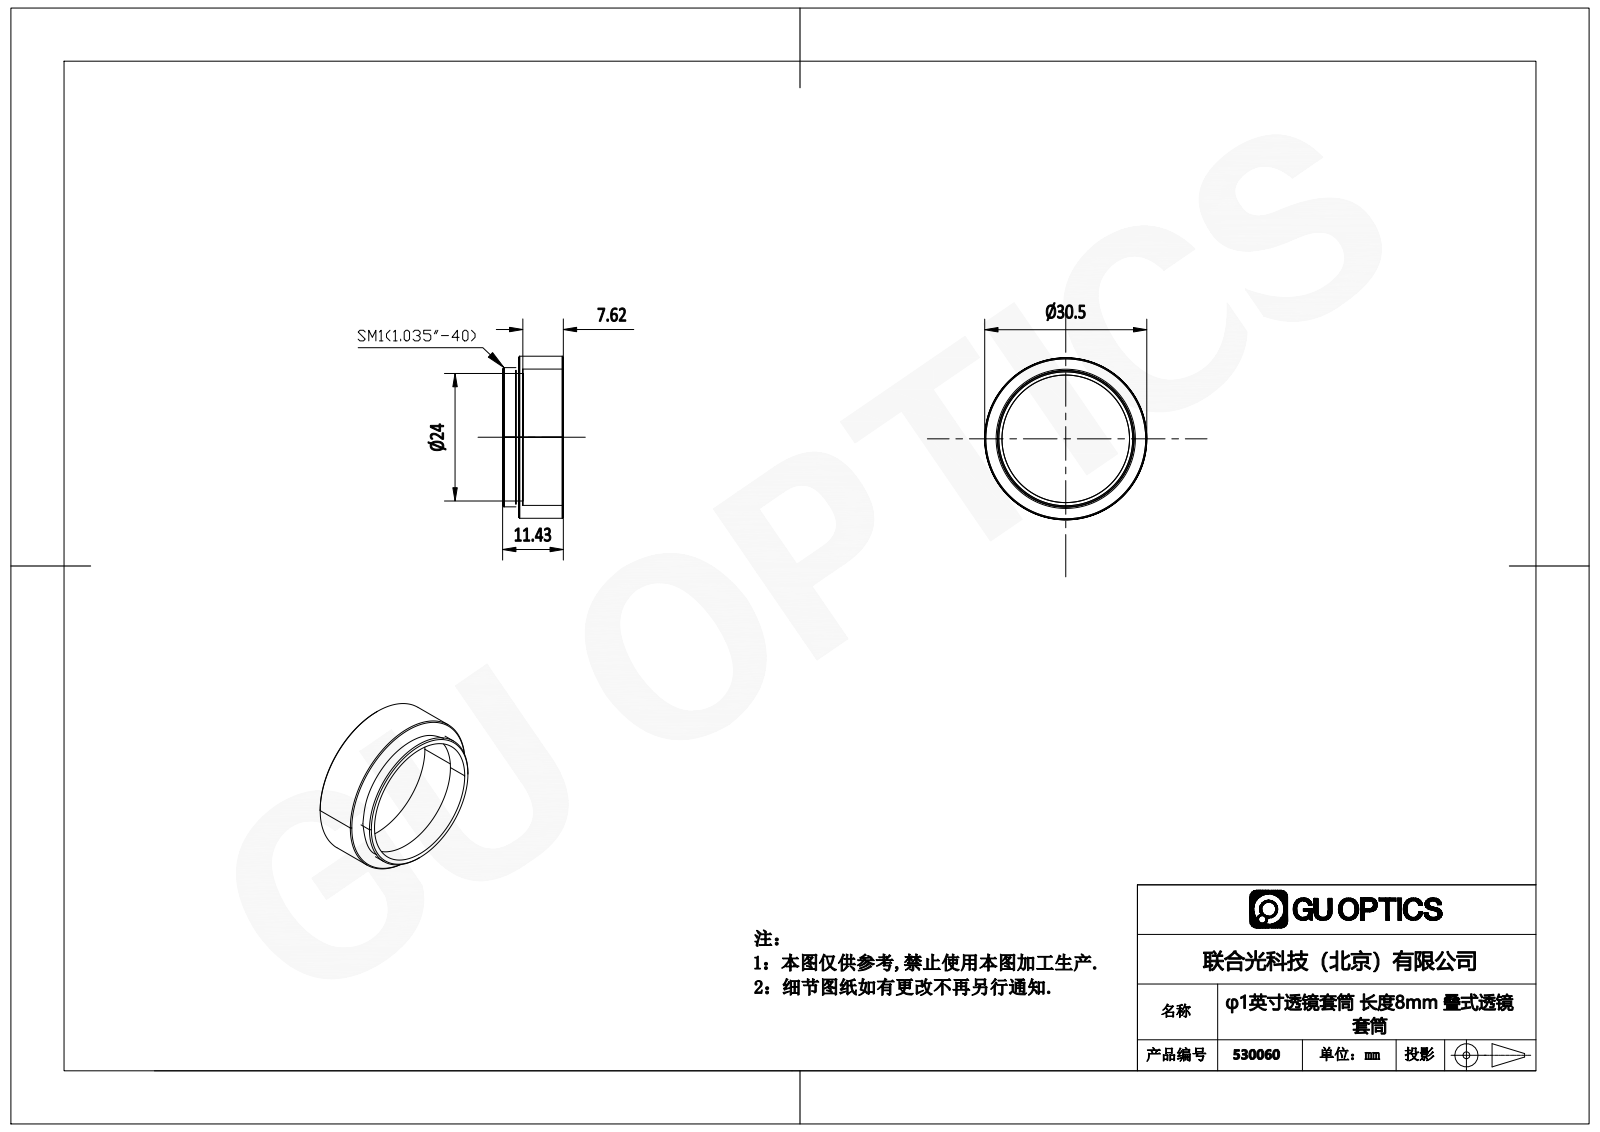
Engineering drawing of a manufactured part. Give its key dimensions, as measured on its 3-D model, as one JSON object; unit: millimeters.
{"part_name": "1.7.1.7_ZTC-1-0.3_SM1标准型0.3英寸层叠式透镜套筒", "step_written_by": "SolidWorks 2018 (AUTOMOTIVE_DESIGN)", "units": "millimeters", "bodies": {"solids": 0, "faces": 36, "planar": 13, "cylindrical": 12, "other": 11}, "overall_size": [30.5, 30.5, 11.42], "round_holes": [[23.01, 1], [24, 1], [25.65, 1]], "round_bosses_or_shafts": [[30.5, 1], [26.2, 1], [25.2, 1]], "face_to_face_distances": [8.42, 2.49, 5.93, 0.49, 2, 7.93, 11.42, 10.93, 8.93, 3]}
